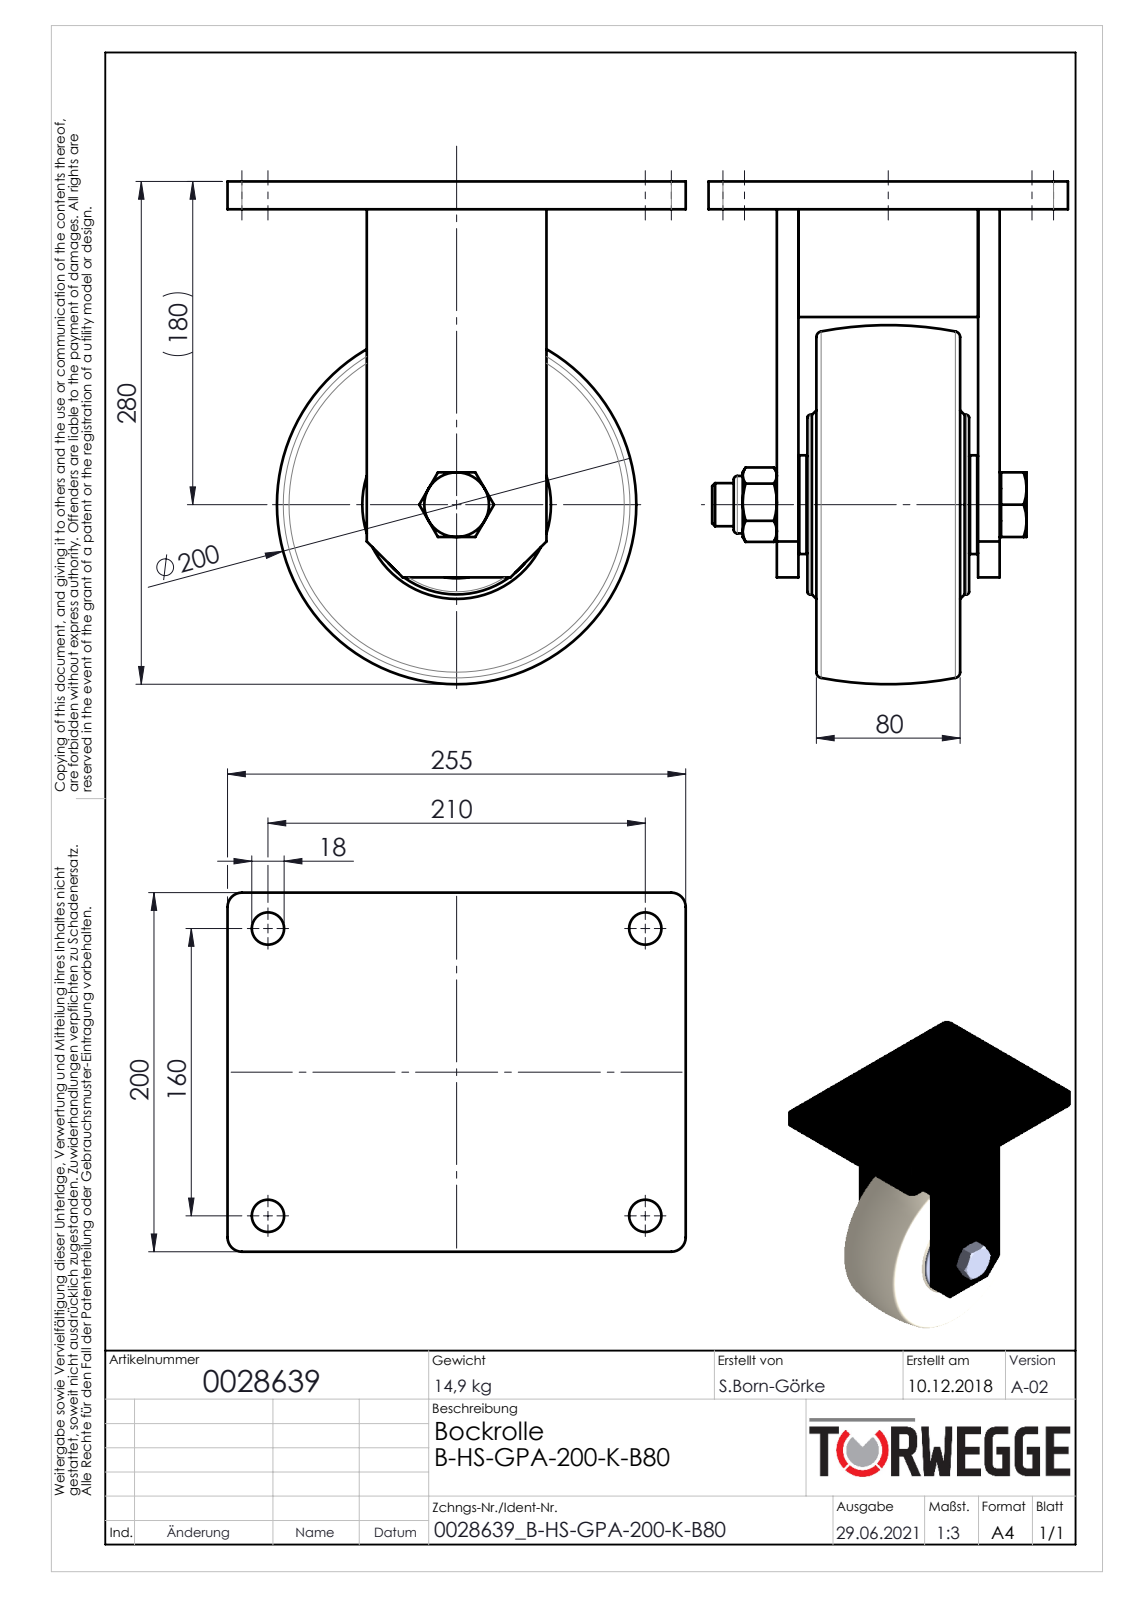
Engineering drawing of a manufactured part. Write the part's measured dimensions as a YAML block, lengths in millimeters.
part_name: "0028639"
step_written_by: "SolidWorks 2020 (AUTOMOTIVE_DESIGN)"
units: millimeters
bodies: {solids: 0, faces: 204, planar: 74, cylindrical: 54, other: 76}
overall_size: [280, 255, 200]
round_holes:
  - {diameter: 18, count: 4}
  - {diameter: 20.75, count: 1}
  - {diameter: 24, count: 1}
  - {diameter: 45, count: 1}
  - {diameter: 46, count: 1}
  - {diameter: 82.07, count: 1}
round_bosses_or_shafts:
  - {diameter: 100, count: 1}
  - {diameter: 62.93, count: 1}
  - {diameter: 55, count: 1}
  - {diameter: 36, count: 1}
  - {diameter: 32, count: 1}
partial_cylinders:
  - {radius: 8, count: 4}
face_to_face_distances: [12, 15.5, 90, 112, 22, 102, 10, 100, 124, 80]
hole_center_spacings: [160, 210, 264.01]
